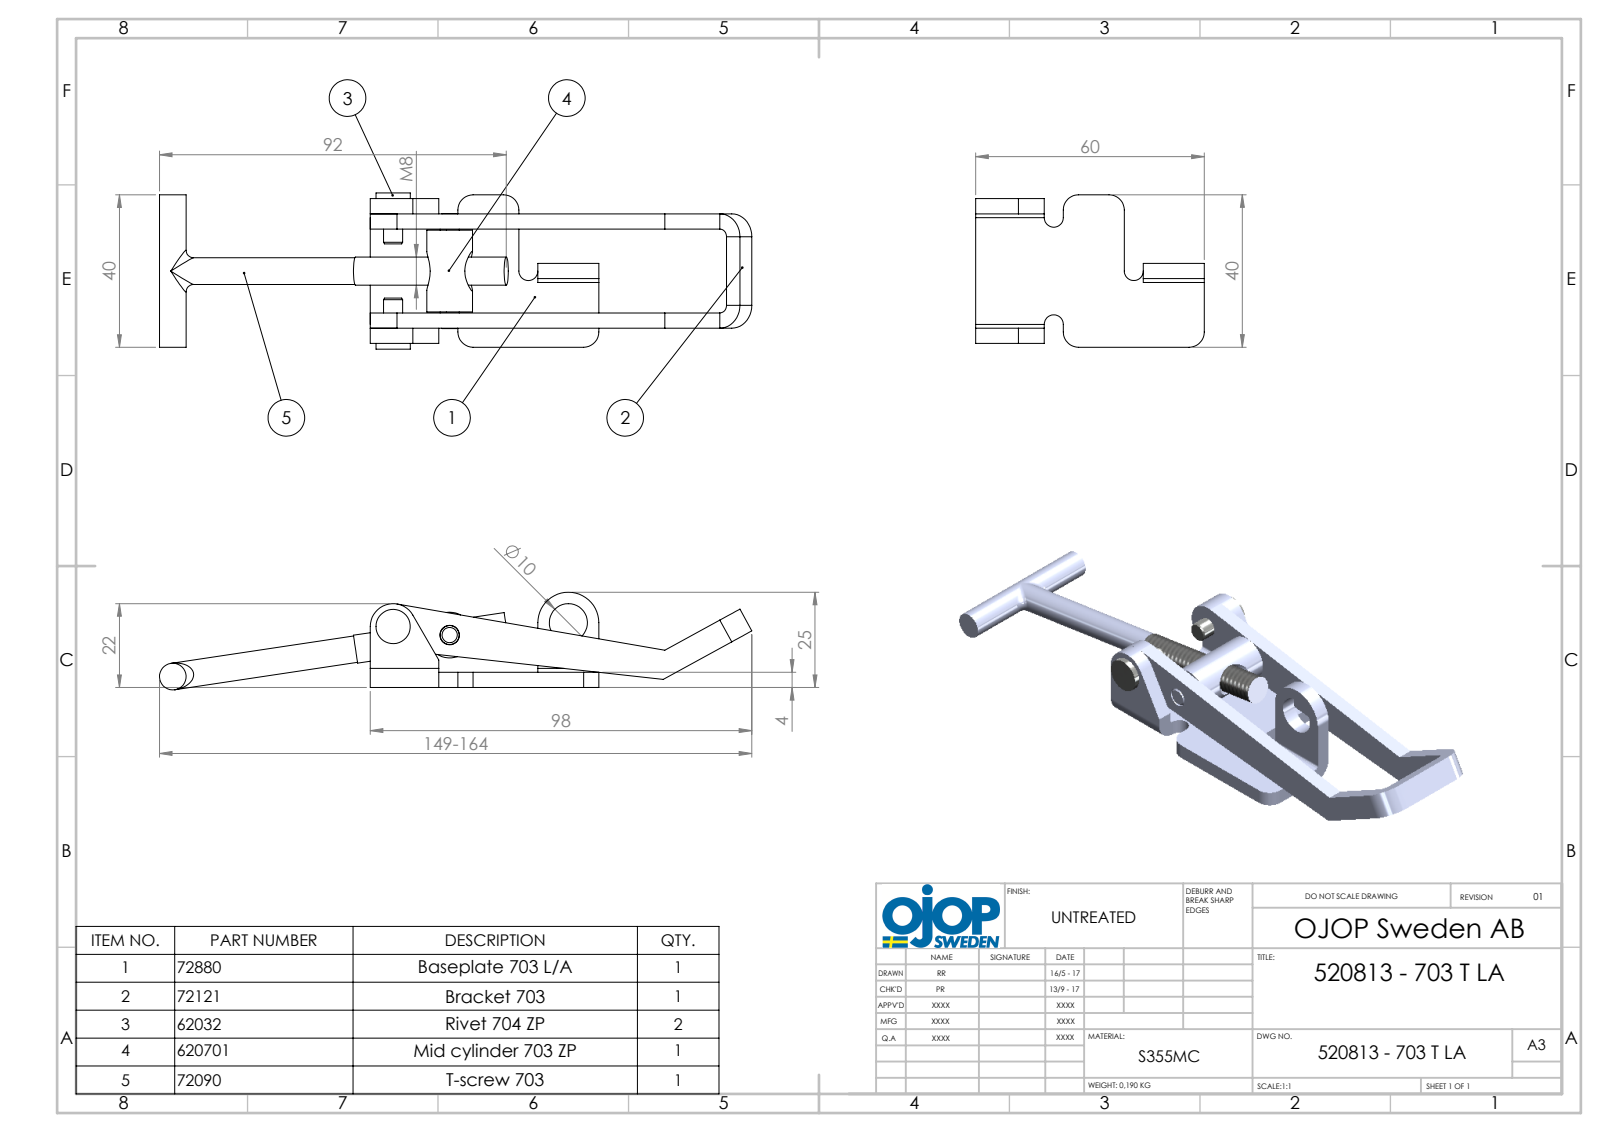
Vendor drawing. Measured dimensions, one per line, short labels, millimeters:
name: 703 - Rulle; 703 - T-skruv; 703- Platta LA; 704 - Rivet Gradin (+2 more)
written by: SolidWorks 2015 (AUTOMOTIVE_DESIGN)
unit: mm
bodies: 6 solids, 145 faces (66 planar, 65 cylindrical, 14 other)
size: 152.02 × 41 × 25.11
volume: 25 100 mm³; area: 17 206 mm²
holes: 2× ⌀5.1, 1× ⌀7.2, 1× ⌀7.7, 1× ⌀10
bosses: 3× ⌀7, 2× ⌀5, 1× ⌀12, 1× ⌀9, 1× ⌀7.4
rounds: 4× R4, 3× R1, 3× R2.5, 3× R5, 3× R6, 2× R2, 1× R8
face distances: 4, 26, 30, 22, 17, 13, 9, 21, 8, 34
hole spacings: 15.01, 31.33, 46.01
